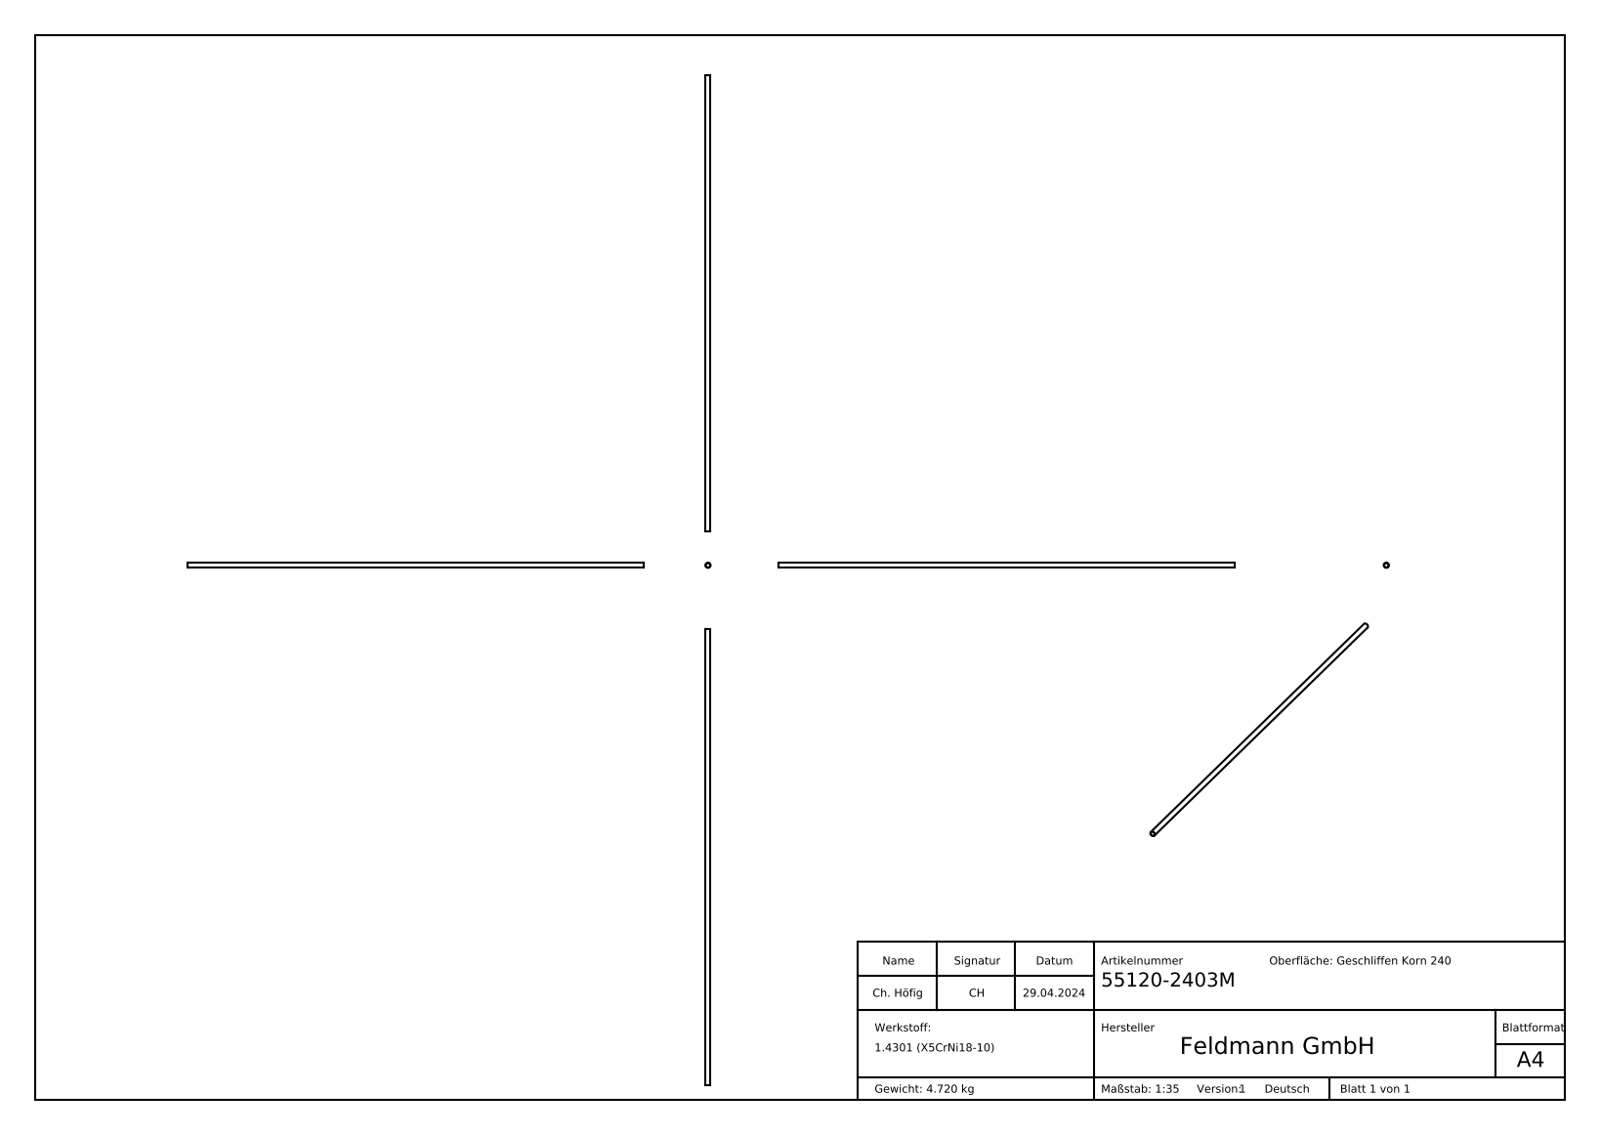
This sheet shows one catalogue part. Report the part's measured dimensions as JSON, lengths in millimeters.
{"part_name": "55120-2403M", "step_written_by": "SolidWorks 2018 (CONFIG_CONTROL_DESIGN)", "units": "millimeters", "bodies": {"solids": 1, "faces": 297, "planar": 141, "cylindrical": 28, "other": 128}, "overall_size": [3000, 33.7, 33.7], "volume_mm3": 597531, "surface_area_mm2": 597937, "round_holes": [[29.7, 1]], "round_bosses_or_shafts": [[33.7, 1]], "partial_cylinders_radius": [[14.95, 1]], "face_to_face_distances": [3000, 1.57, 2.24, 1.78, 2.41, 0.73, 1.23, 2.61, 0.65, 0.79]}
